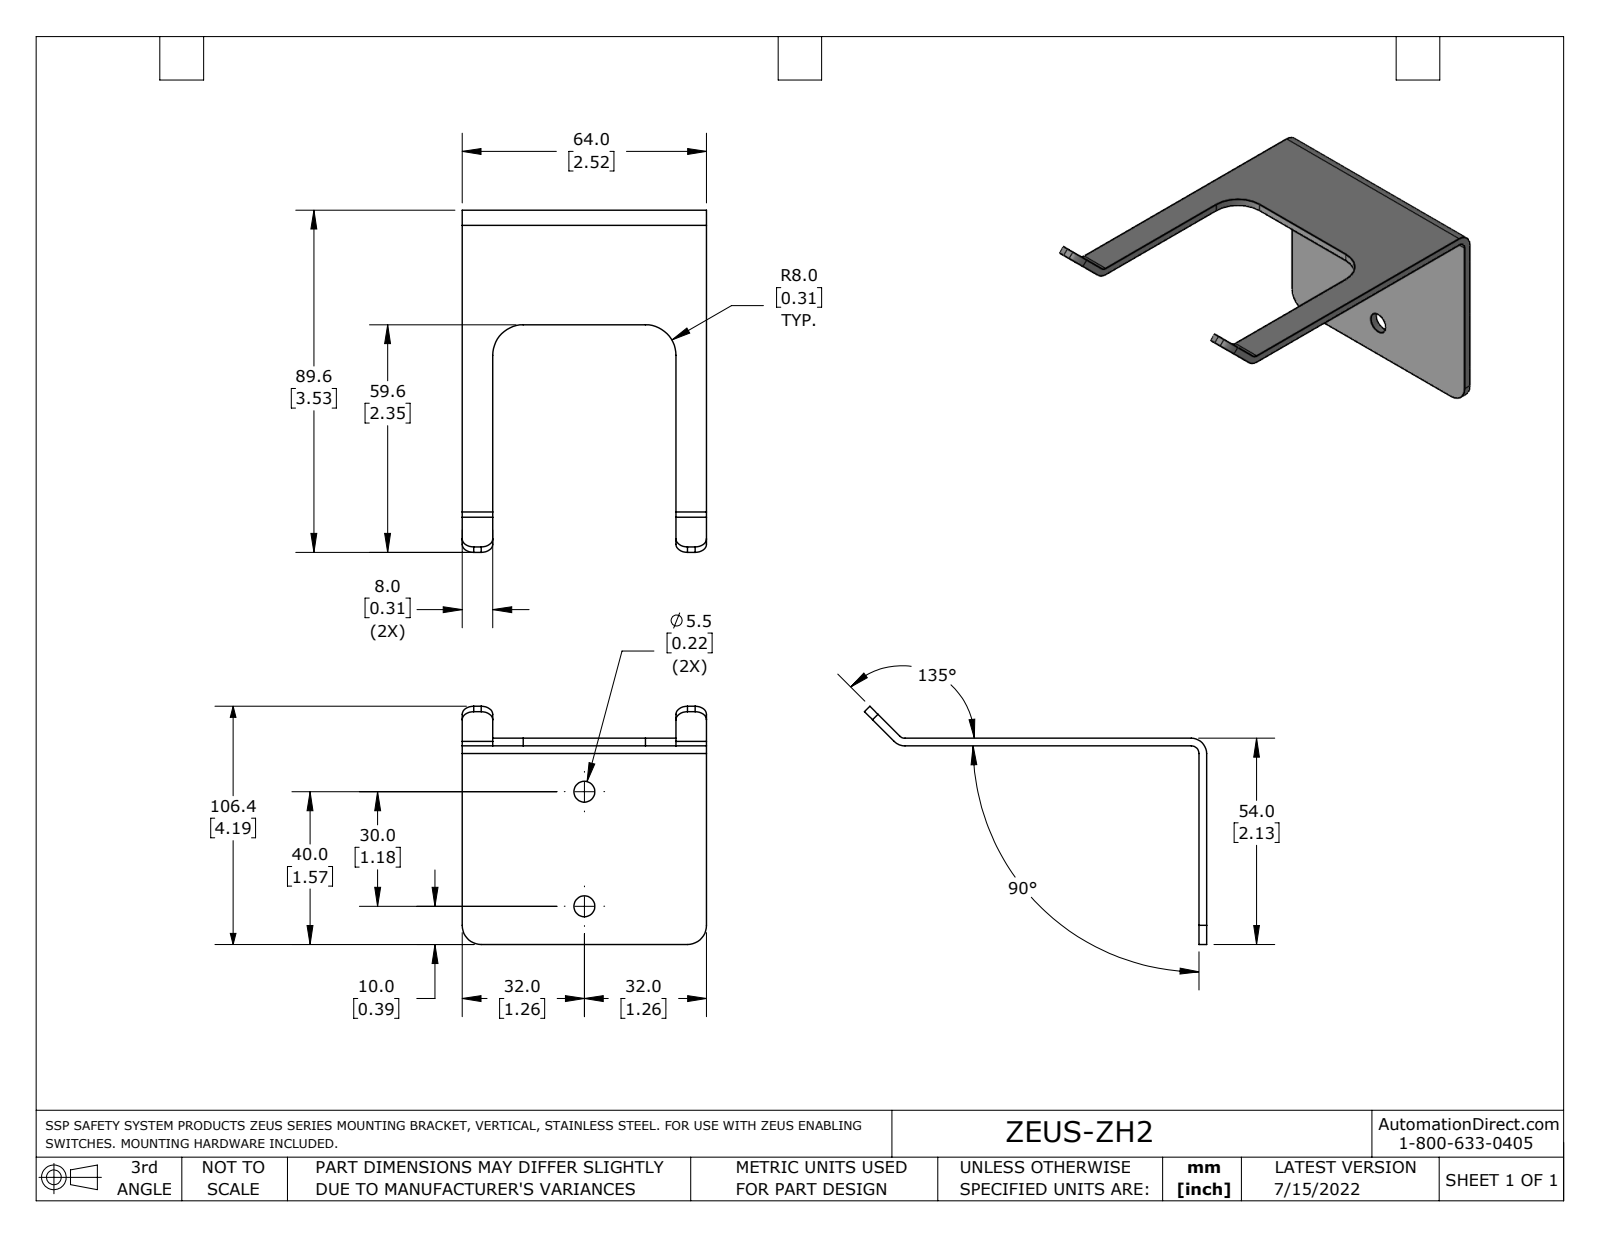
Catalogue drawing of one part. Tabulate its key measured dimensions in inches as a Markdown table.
| quantity | value |
| --- | --- |
| part name | ZEUS-ZH2 |
| STEP written by | SolidWorks 2021 (AUTOMOTIVE_DESIGN) |
| units | inches |
| bodies | 1 solid, 32 faces (16 planar, 16 cylindrical, 0 other) |
| overall size | 4.191 × 2.52 × 2.236 |
| volume | 0.748 in³ |
| surface area | 20.71 in² |
| round holes (diameter × count) | 0.217 × 2 |
| partial cylindrical surfaces (radius × count) | 0.118 × 4, 0.079 × 2, 0.157 × 2, 0.197 × 2, 0.315 × 2 |
| main face-to-face distances | 0.079, 2.52, 0.315, 2.205, 2.126, 2.047, 1.89, 1.102, 1.181 |
| hole center spacings | 1.181 |
